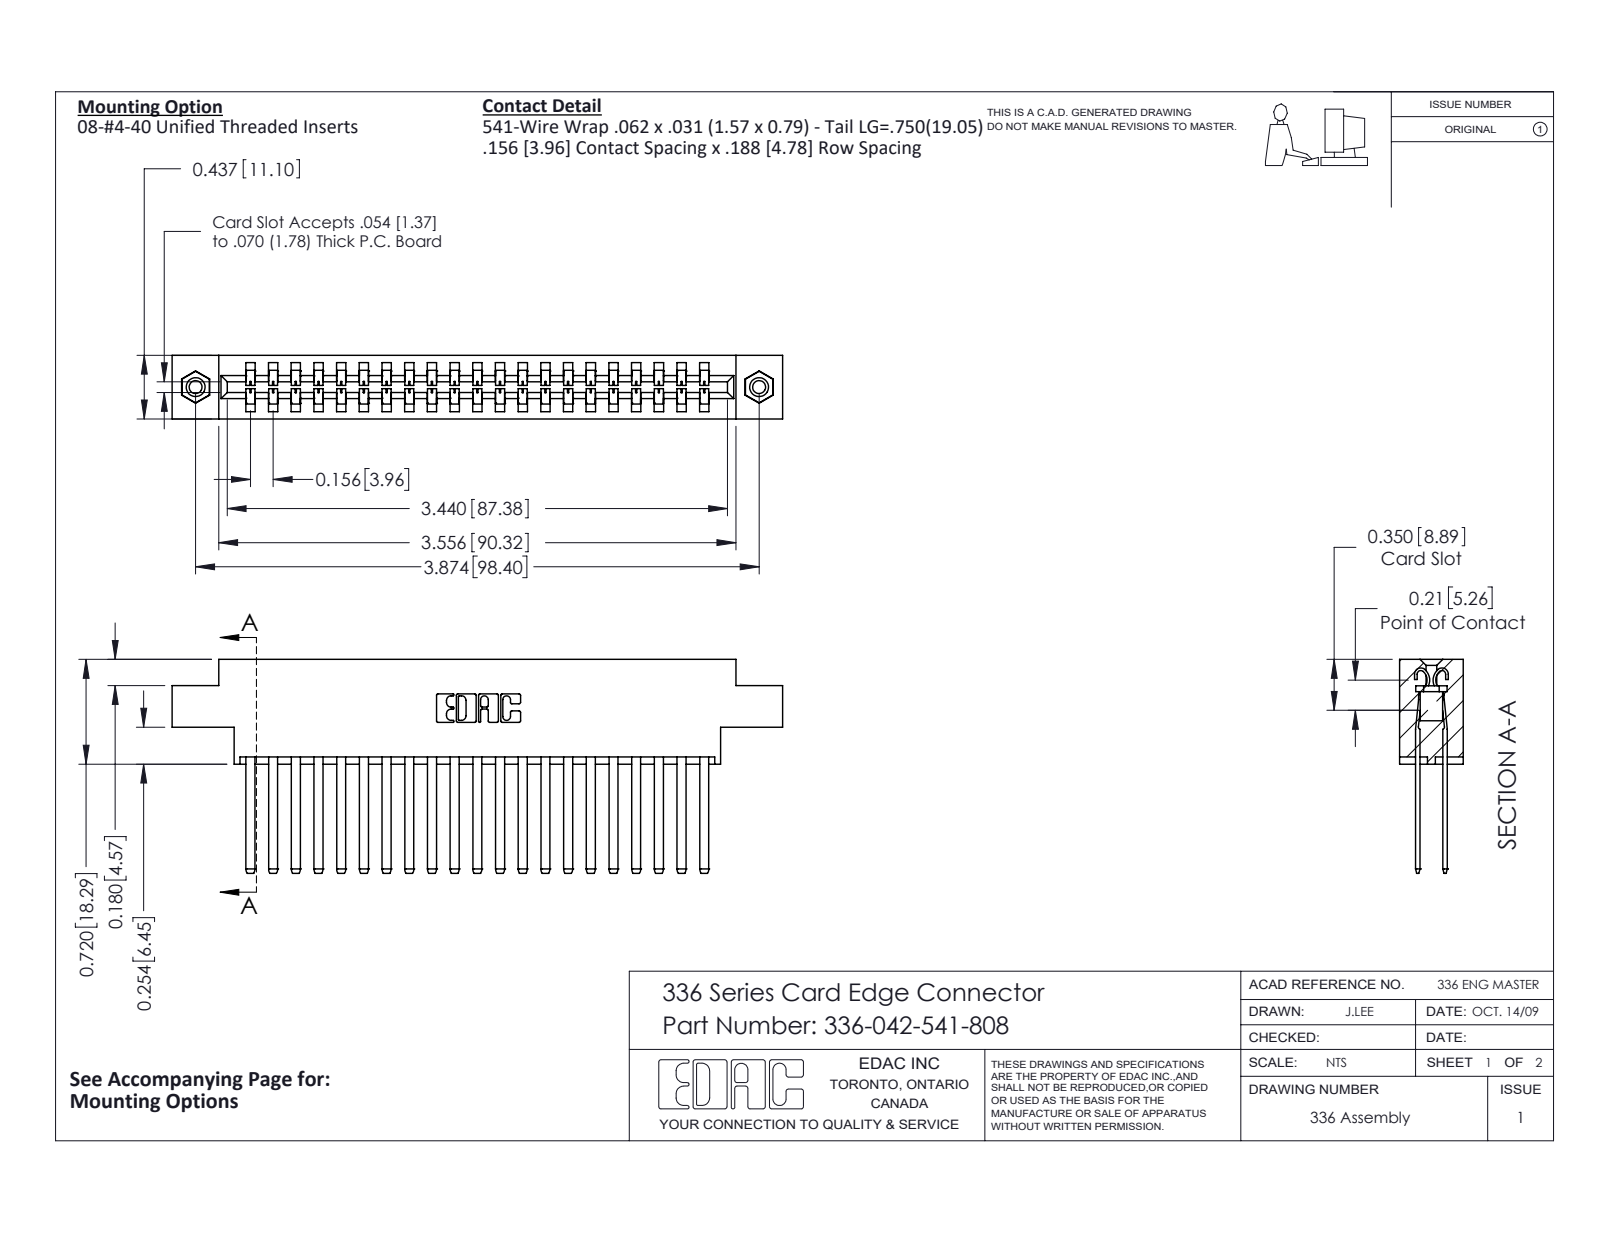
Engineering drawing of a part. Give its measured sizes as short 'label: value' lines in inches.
name: 345-250-001_345-250-003-102; 336-042-541-808; 336-290-001_336-290-541; 336 Part_Offset - .156 Dia - TI
written by: SolidWorks 2020 (CONFIG_CONTROL_DESIGN)
unit: in
bodies: 45 solids, 1942 faces (1198 planar, 728 cylindrical, 16 other)
size: 4.197 × 1.47 × 0.437
volume: 0.962 in³; area: 30.75 in²
holes: 2× ⌀0.089, 2× ⌀0.125, 2× ⌀0.156
bosses: 2× ⌀0.155
rounds: 84× R0.004, 42× R0.056, 22× R0.01, 6× R0.007, 6× R0.031, 4× R0.022, 4× R0.04, 3× R0.026
face distances: 0.188, 0.328, 0.14, 0.297, 0.109, 0.031, 0.437, 0.033, 0.181, 0.146
hole spacings: 3.874
